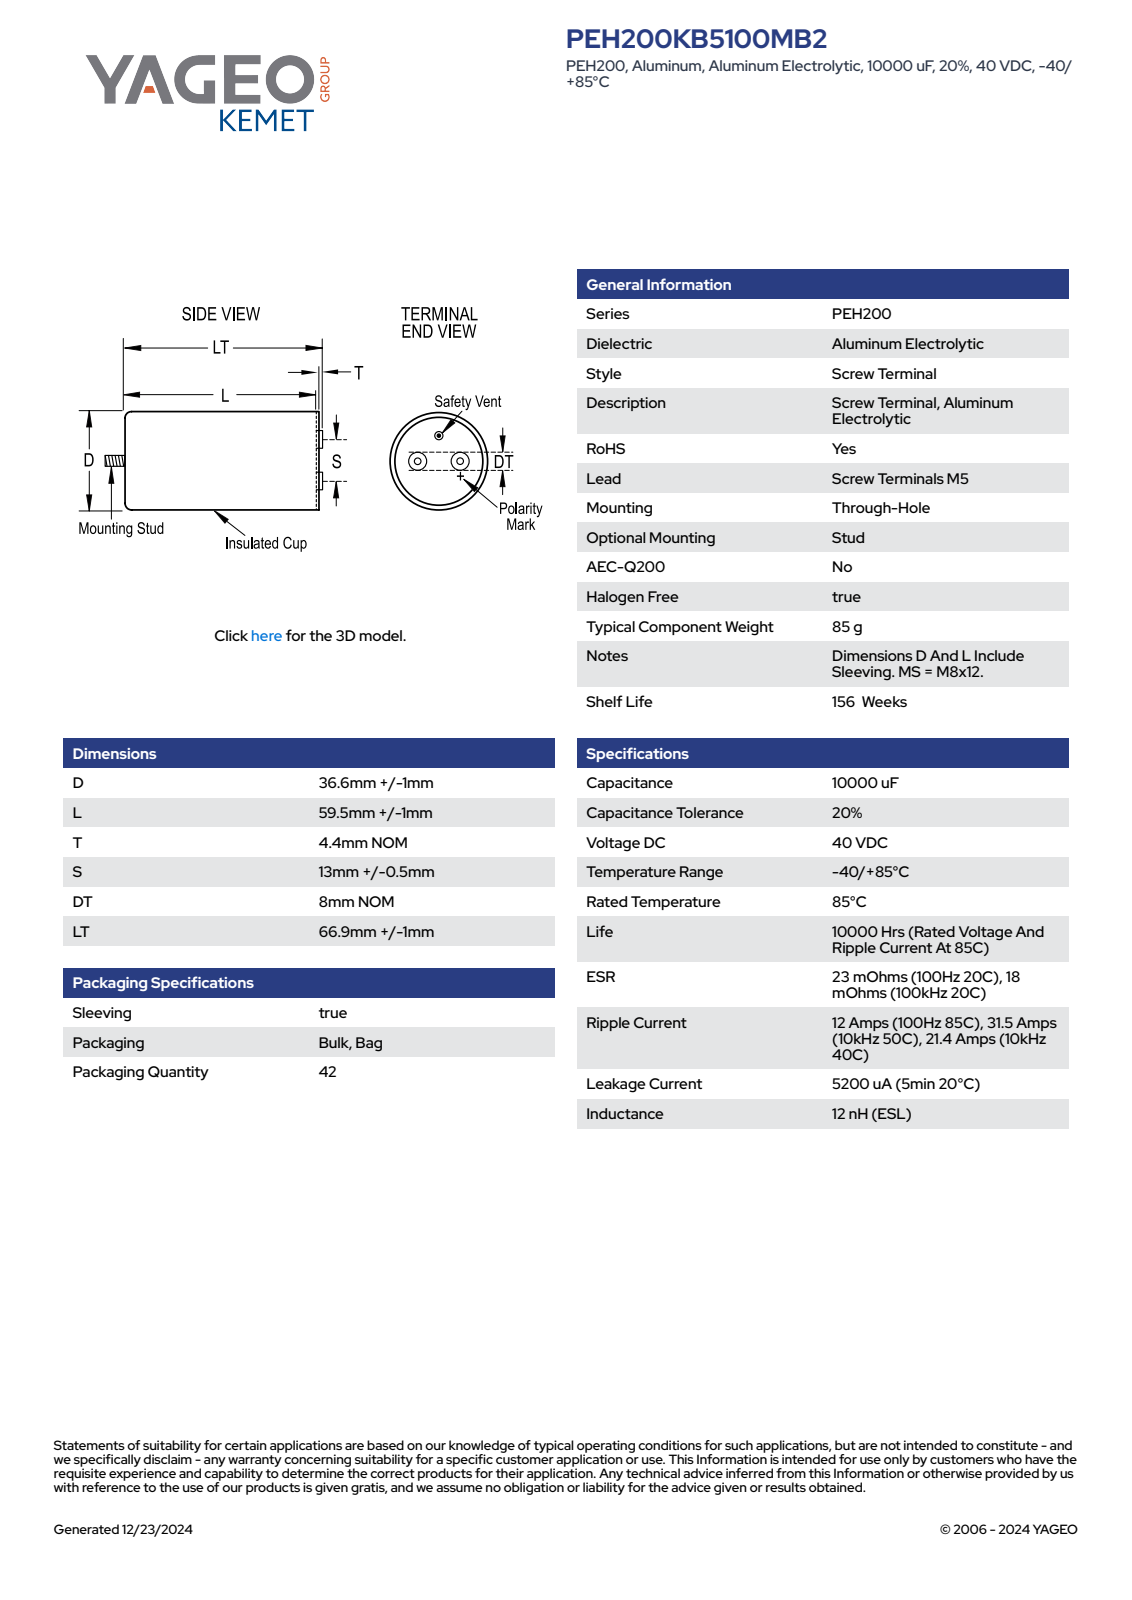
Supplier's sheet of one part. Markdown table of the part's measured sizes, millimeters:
| quantity | value |
| --- | --- |
| part name | Round_Terminal; CARCS_D37.6L60.5S13T4.4; Stud8; Can_Round_6 |
| STEP written by | SolidWorks 2014 (AUTOMOTIVE_DESIGN) |
| units | millimeters |
| bodies | 4 solids, 147 faces (54 planar, 61 cylindrical, 32 other) |
| overall size | 79.9 × 37.6 × 37.6 |
| volume | 68 182 mm³ |
| surface area | 11 058 mm² |
| round holes (diameter × count) | 5 × 2, 35.6 × 1 |
| round bosses / shafts (diameter × count) | 8 × 3, 37.6 × 1, 7.7 × 1 |
| partial cylindrical surfaces (radius × count) | 18.79 × 1 |
| main face-to-face distances | 60.5, 3, 63.5, 4.4, 7.4, 67.9, 1, 79.9, 75.5, 72.5 |
| hole center spacings | 6.5, 13 |
